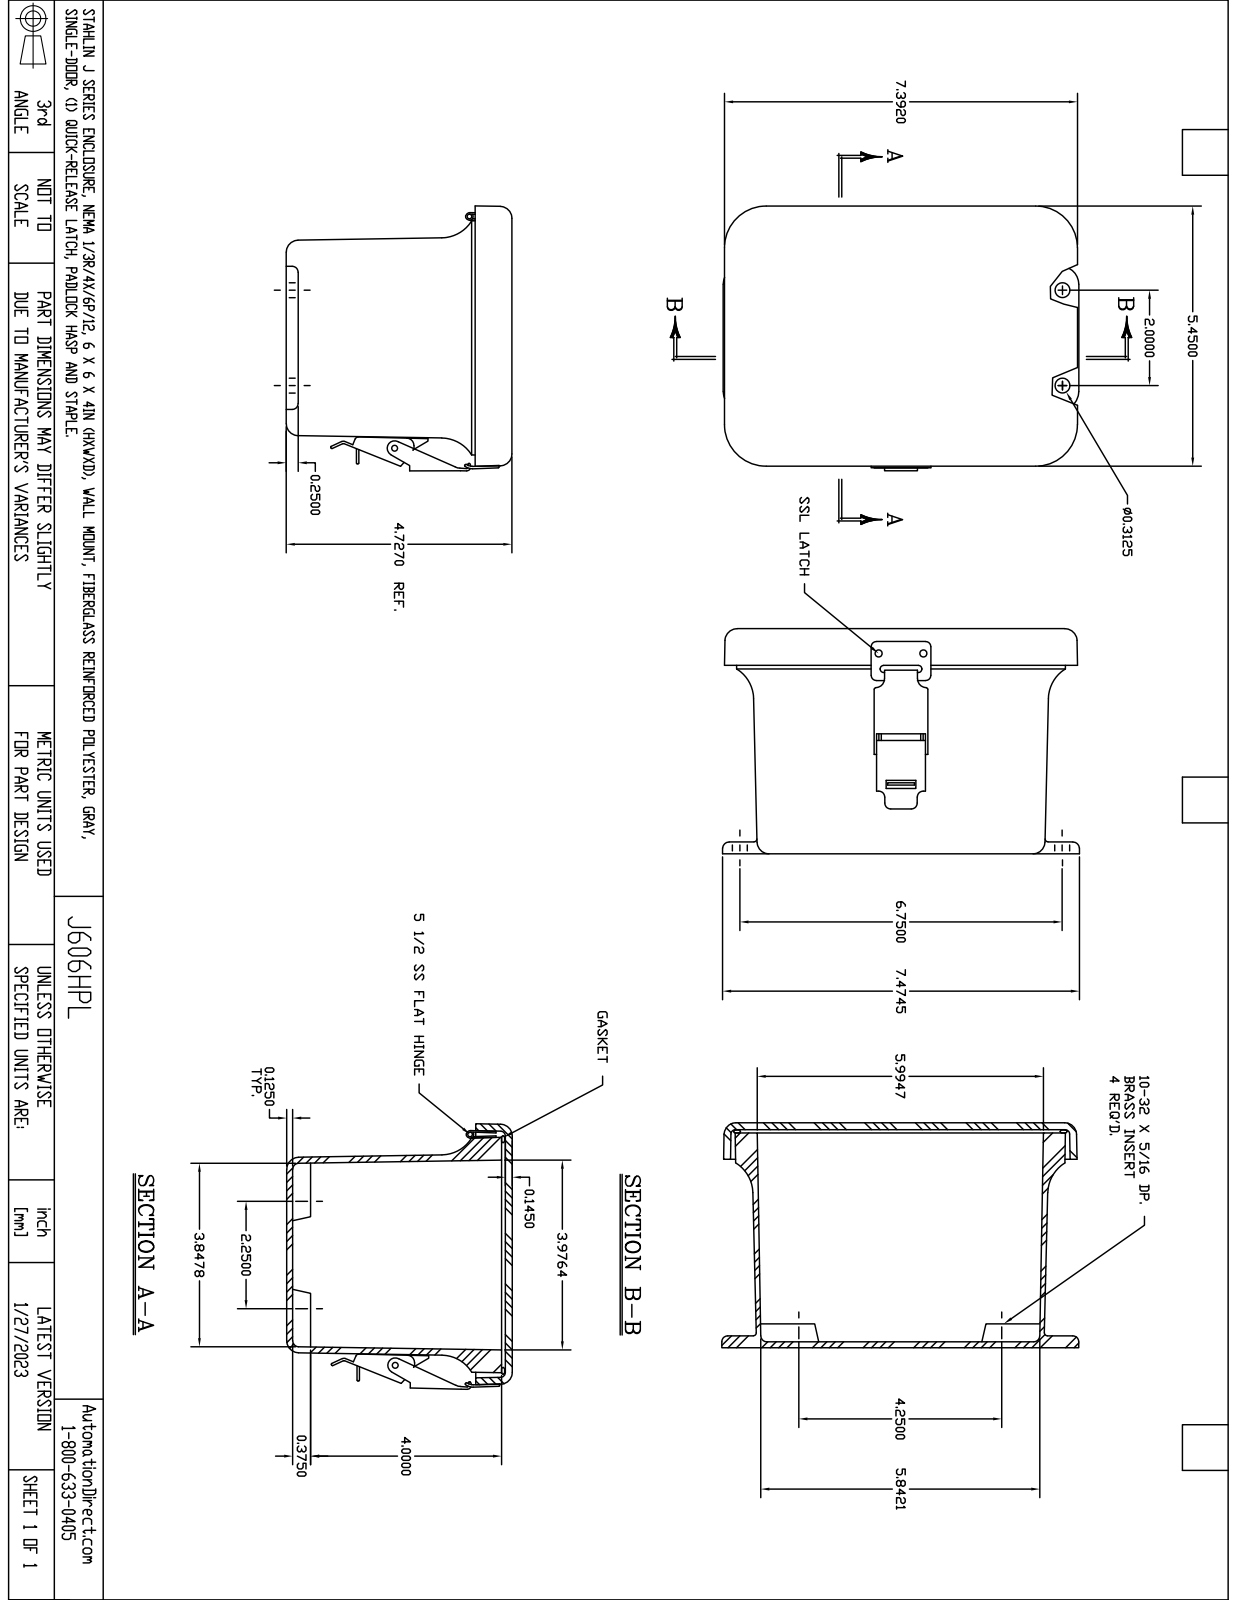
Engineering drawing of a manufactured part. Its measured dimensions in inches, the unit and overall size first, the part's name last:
Units: inches
Overall size (bounding box): 7.614 × 7.525 × 4.841
Round holes (diameter × count): ⌀0.14 ×11, ⌀0.131 ×5, ⌀0.152 ×5, ⌀0.104 ×4, ⌀0.156 ×4, ⌀0.218 ×4, ⌀0.13 ×2, ⌀0.135 ×2, ⌀0.085 ×1, ⌀0.085 ×1, ⌀0.375 ×1
Round bosses / shafts (diameter × count): ⌀0.125 ×7, ⌀0.25 ×5, ⌀0.27 ×4, ⌀0.125 ×2, ⌀0.3 ×1, ⌀0.17 ×1, ⌀0.155 ×1, ⌀0.155 ×1
Partial cylindrical surfaces — rounded edges, fillets, slot ends (radius × count): R0.031 ×20, R0.015 ×12, R0.125 ×12, R0.25 ×12, R0.045 ×8, R0.03 ×6, R0.022 ×5, R0.06 ×4
Main face-to-face distances: 0.147, 4.693, 4.841, 0.125, 4.569, 4.716, 0.152, 4.5, 4.625, 0.069
Hole centre spacings: 5.308, 0.937, 1.37, 2.5, 4.25, 6.187, 7.38, 0.75
Volume: 38.1 in³ · Surface area: 517.3 in²
Bodies: 25 solids, 631 faces (249 planar, 258 cylindrical, 124 other)
Part name (STEP PRODUCT): M606HPL
STEP written by: SolidWorks 2018 (AUTOMOTIVE_DESIGN)
